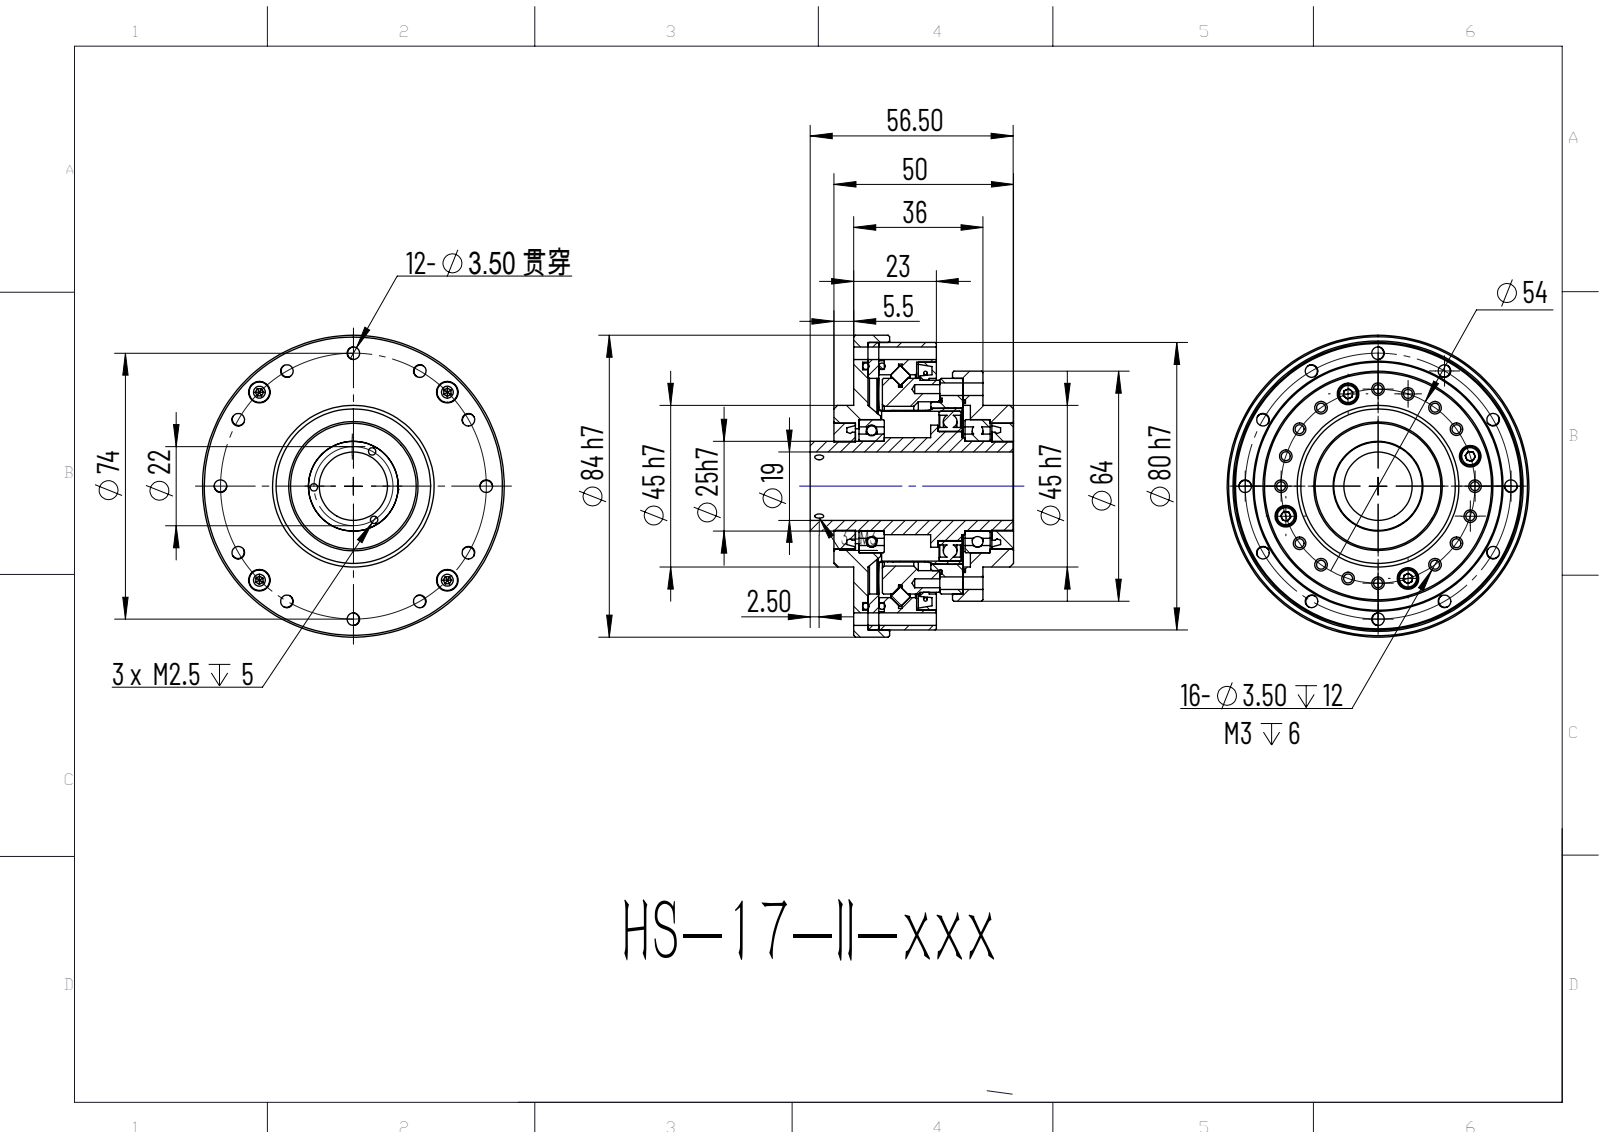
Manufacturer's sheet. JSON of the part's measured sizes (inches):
{"part_name": "HS-17-II; hexagon socket button head screws gb_GB_SOCKET_TYPE7 M3X10-C; ??25X35X6; ????-STXB-17050 (+8 more)", "step_written_by": "ONSHAPE BY PTC INC, 1.201 (AP242_MANAGED_MODEL_BASED_3D_ENGINEERING_MIM_LF)", "units": "inches", "bodies": {"solids": 98, "faces": 1324, "planar": 601, "cylindrical": 333, "other": 390}, "overall_size": [3.307, 3.307, 2.228], "volume_in3": 8.032, "surface_area_in2": 176.6, "round_holes": [[0.138, 48], [0.098, 27], [0.134, 8], [0.236, 8], [0.081, 3], [0.063, 1], [0.094, 1], [0.169, 1], [0.748, 1], [0.984, 1], [1.193, 1], [1.26, 1]], "round_bosses_or_shafts": [[0.157, 36], [0.118, 8], [0.217, 4], [3.307, 1], [3.15, 1], [2.559, 1], [2.551, 1], [2.52, 1]], "partial_cylinders_radius": [[0.08, 36]], "face_to_face_distances": [0.157, 0.217, 0.276, 0.63, 0.118, 0.256, 1.417, 0.039, 0.374, 0.748], "hole_center_spacings": [1.063, 1.503, 1.894, 0.657, 0.965, 1.457, 2.022, 0.332]}
